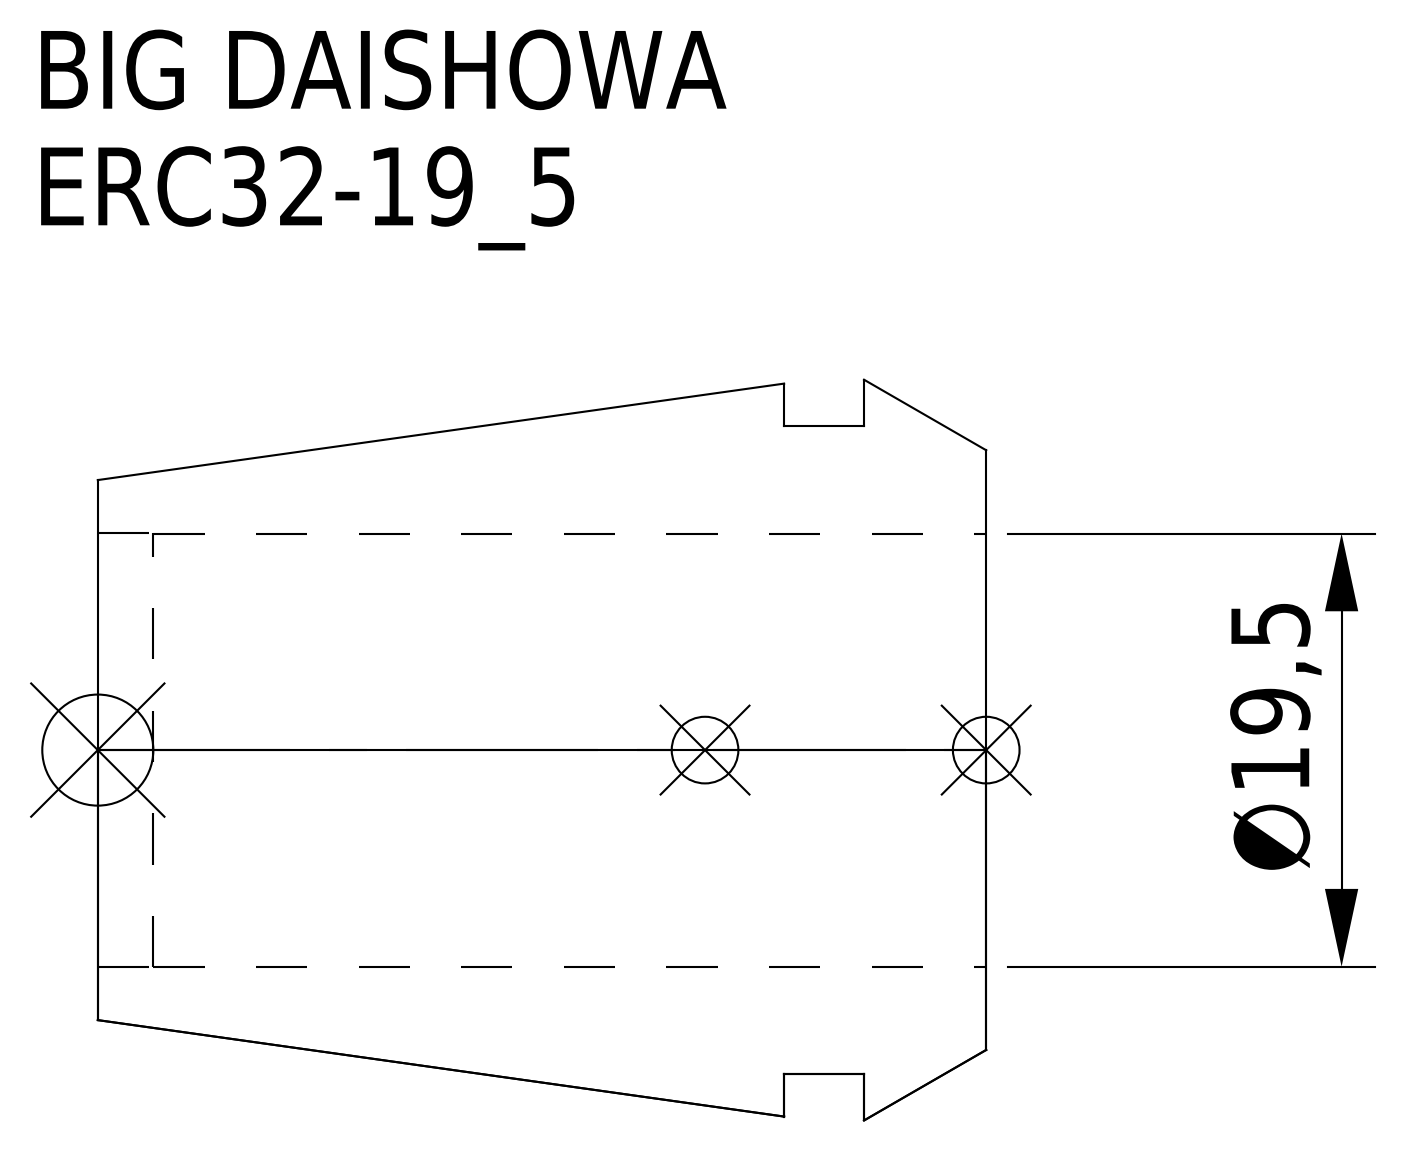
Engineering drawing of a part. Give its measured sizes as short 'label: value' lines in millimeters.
name: ERC32-19_5
written by: CREO PARAMETRIC BY PTC INC, 2016380 (AUTOMOTIVE_DESIGN)
unit: mm
bodies: 1 solid, 15 faces (5 planar, 6 cylindrical, 4 other)
size: 40 × 33.35 × 33.35
volume: 14 493 mm³; area: 7 022 mm²
holes: 1× ⌀19.5, 1× ⌀19.55
bosses: 1× ⌀29.2
face distances: 5.5, 9.1, 3.6, 40, 34.5, 30.9, 37.5, 32, 28.4, 2.5
